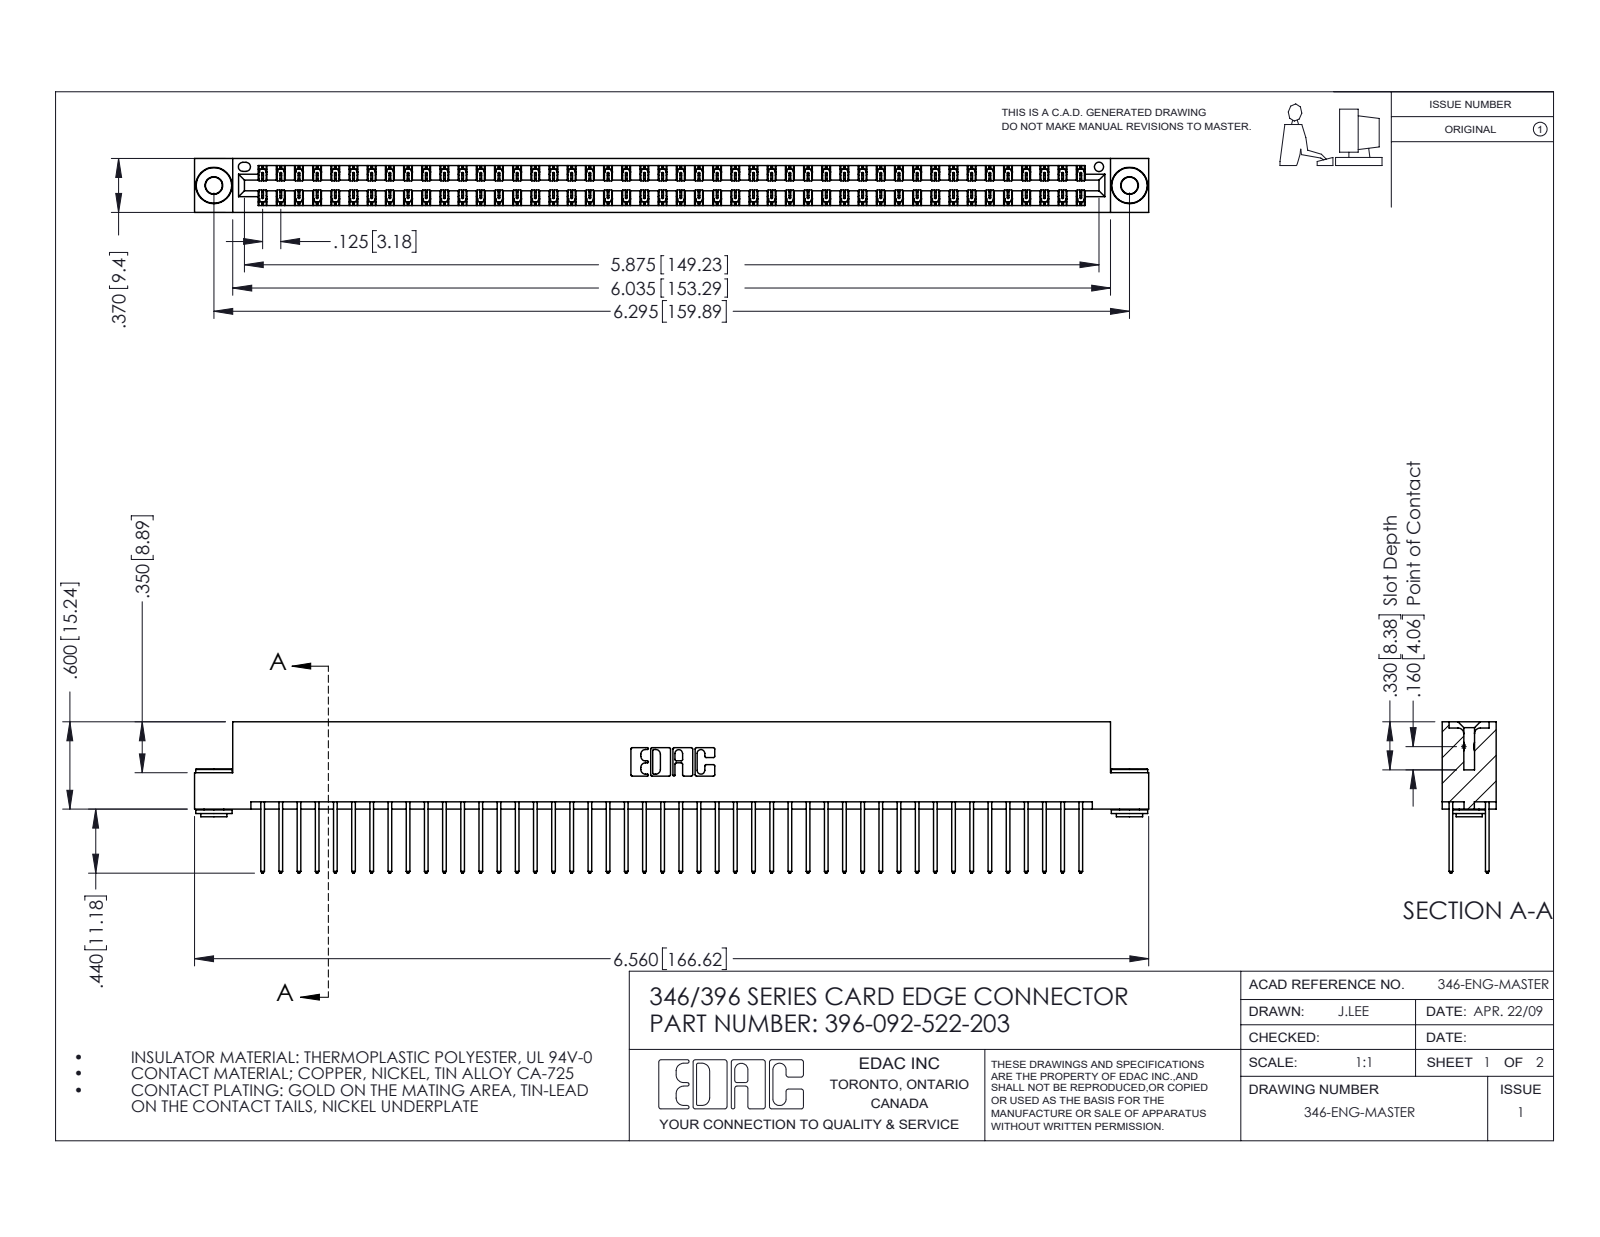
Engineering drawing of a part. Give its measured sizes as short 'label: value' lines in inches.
name: 346 Part_Flush Mounting Lugs - 0.156 Dia-TH; 345-250-002_345-250-002-102; 396-092-522-203; 345-292-001_345-293-122
written by: SolidWorks 2016 (CONFIG_CONTROL_DESIGN)
unit: in
bodies: 95 solids, 4944 faces (3306 planar, 1630 cylindrical, 8 other)
size: 6.56 × 1.04 × 0.37
volume: 1.009 in³; area: 37.35 in²
holes: 2× ⌀0.116, 2× ⌀0.156, 1× ⌀0.064
bosses: 2× ⌀0.25, 2× ⌀0.18, 2× ⌀0.136
rounds: 138× R0.006, 92× R0.01, 22× R0.01, 6× R0.007, 6× R0.031, 3× R0.026, 2× R0.014, 2× R0.022
face distances: 0.048, 0.322, 0.25, 0.025, 0.37, 0.072, 0.298, 0.275, 0.148, 0.222
hole spacings: 0.246, 6.086, 6.295
